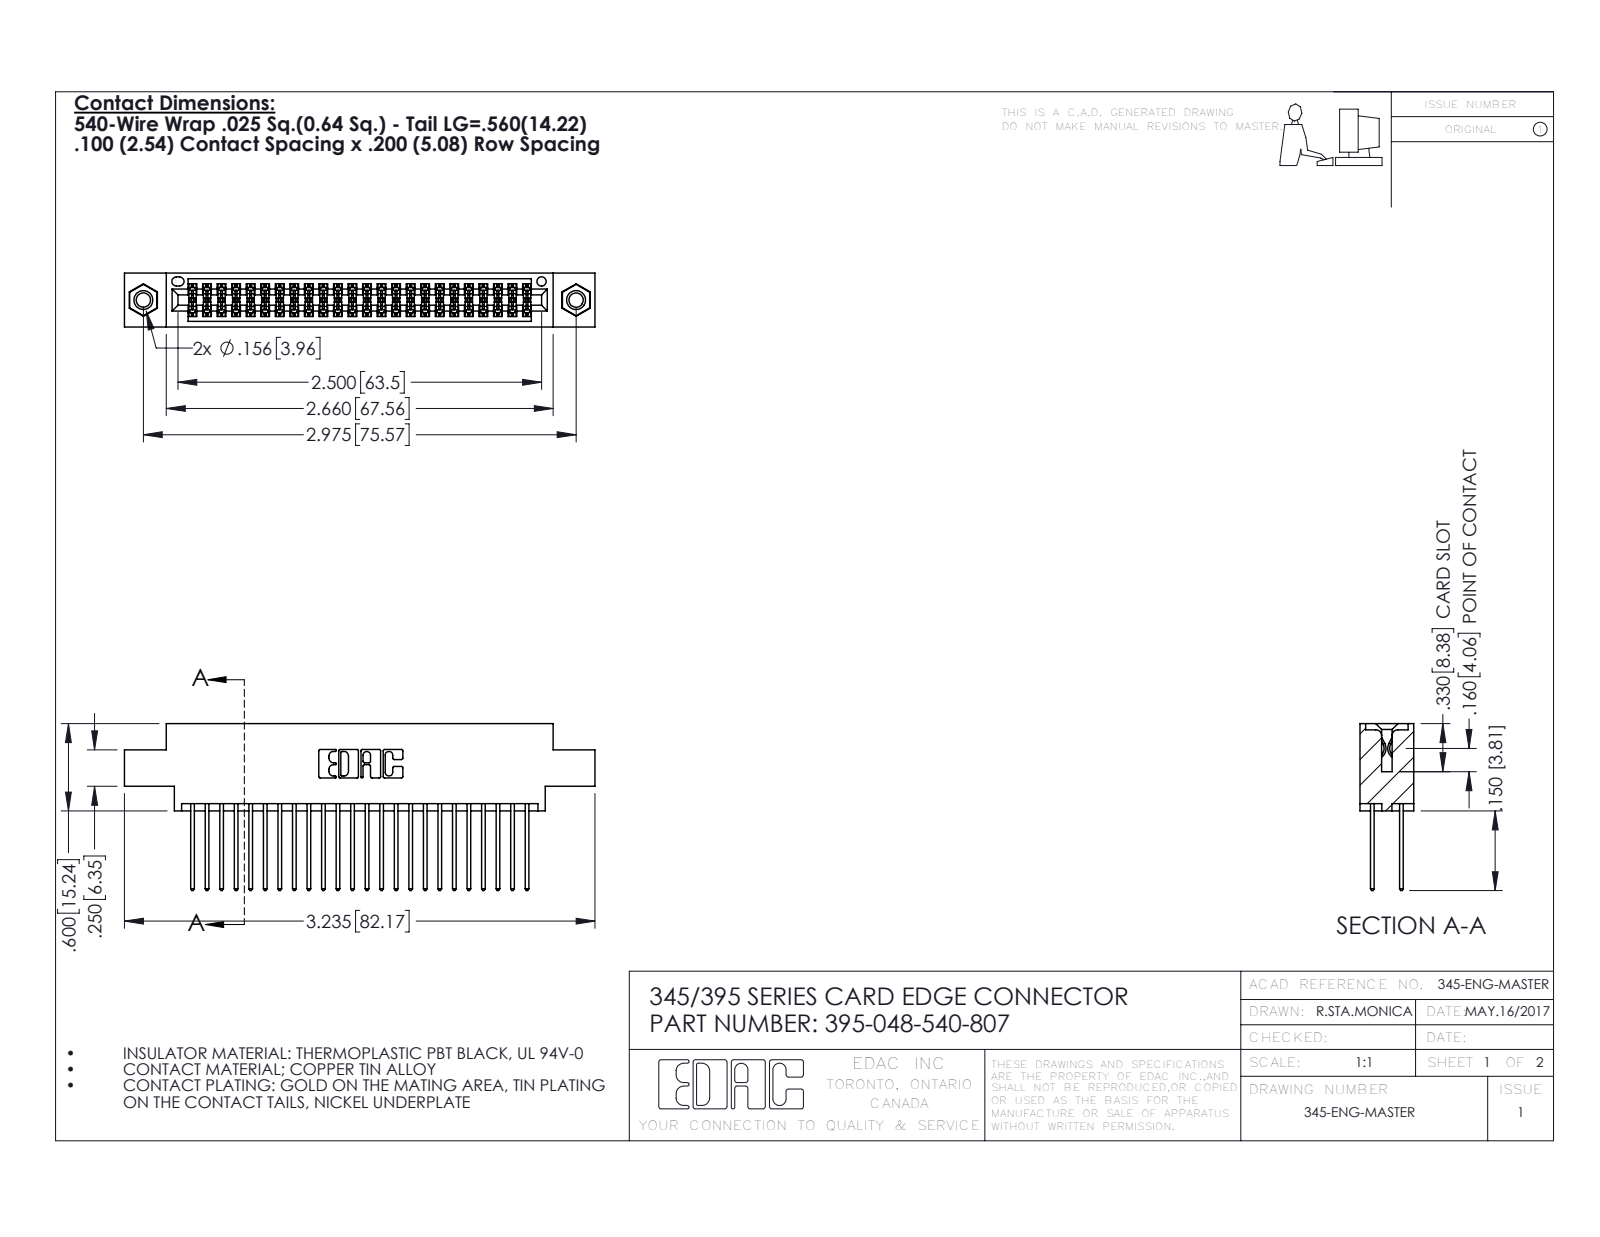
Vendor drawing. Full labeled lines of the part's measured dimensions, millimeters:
Part name (STEP PRODUCT): 345-250-001_345-250-005-103; 395-048-540-807; 345 Part_0.170 Offset - 0.156 Dia-TI; 345-292-001_345-293-140
STEP written by: SolidWorks 2016 (CONFIG_CONTROL_DESIGN)
Units: millimetres
Bodies: 51 solids, 2590 faces (1700 planar, 874 cylindrical, 16 other)
Overall size (bounding box): 82.2 × 29.1 × 9.4
Volume: 7 870 mm³ · Surface area: 12 300 mm²
Round holes (diameter × count): ⌀2.5 ×2, ⌀3.2 ×2, ⌀4 ×2, ⌀1.6 ×1
Round bosses / shafts (diameter × count): ⌀3.9 ×2
Partial cylindrical surfaces — rounded edges, fillets, slot ends (radius × count): R0.2 ×72, R0.3 ×48, R0.3 ×22, R0.2 ×6, R0.8 ×6, R0.7 ×3, R0.4 ×2, R0.5 ×2
Main face-to-face distances: 1.8, 7.6, 5.1, 2.5, 6.9, 0.6, 9.4, 5.7, 4.4, 3.8
Hole centre spacings: 6.9, 69.6, 75.6
